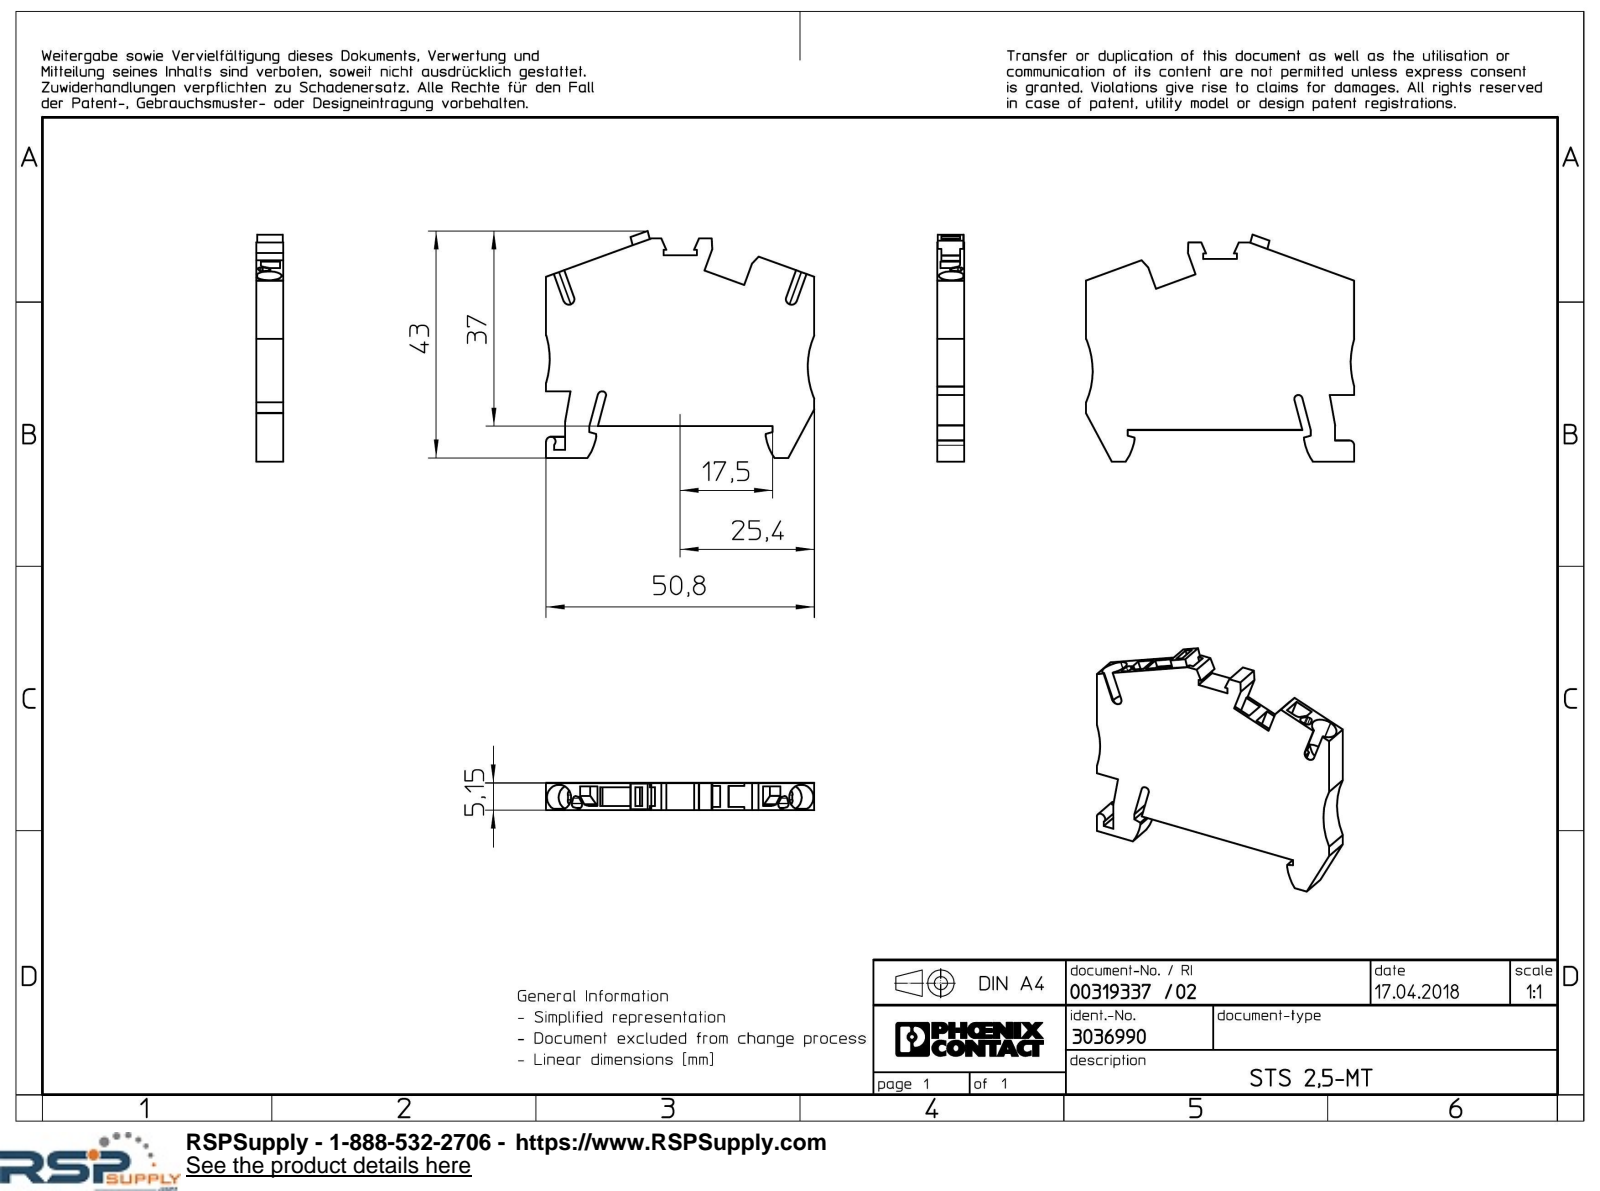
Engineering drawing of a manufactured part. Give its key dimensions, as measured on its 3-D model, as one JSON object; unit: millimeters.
{"part_name": "STS25-MT-Select", "step_written_by": "Creo Elements/Direct Modeling 18.1I 14-Aug-2016 (C) Parametric Technology GmbH (AUTOMOTIVE_DESIGN)", "units": "millimeters", "bodies": {"solids": 1, "faces": 172, "planar": 131, "cylindrical": 35, "other": 6}, "overall_size": [50.8, 42.97, 5.15], "volume_mm3": 7304, "surface_area_mm2": 5532, "partial_cylinders_radius": [[1, 10], [0.3, 4], [0.6, 4], [2.4, 4], [0.5, 2], [1.75, 2], [9.5, 2], [15, 2]], "face_to_face_distances": [5.15, 4.85, 3.15, 0.65, 4, 0.57, 0.58, 4.57, 4.58, 8]}
